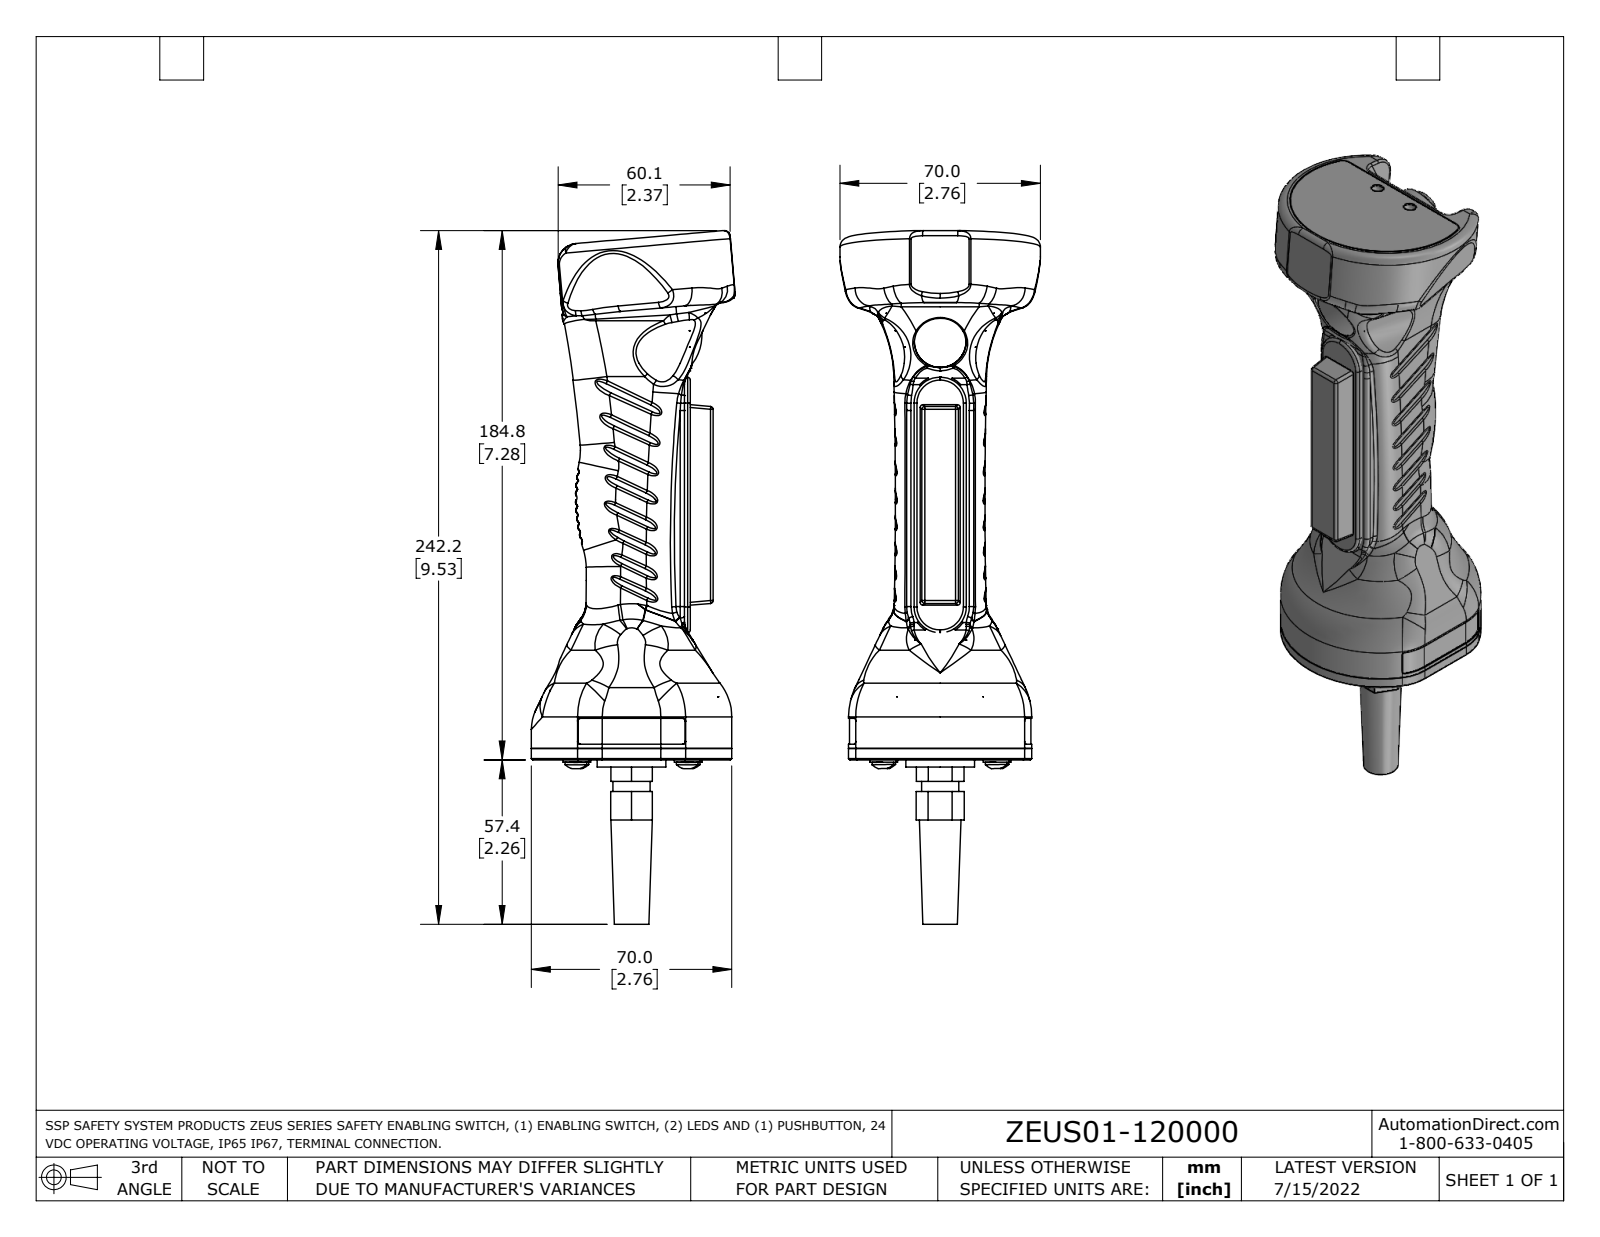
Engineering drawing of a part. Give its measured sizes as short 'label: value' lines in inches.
name: ZEUS01-120000
written by: SolidWorks 2021 (AUTOMOTIVE_DESIGN)
unit: in
bodies: 18 solids, 1363 faces (467 planar, 452 cylindrical, 444 other)
size: 9.535 × 2.803 × 2.756
volume: 23.35 in³; area: 121.2 in²
holes: 4× ⌀0.132, 4× ⌀0.169, 4× ⌀0.177, 4× ⌀0.197, 2× ⌀0.098, 2× ⌀0.11, 2× ⌀0.165, 2× ⌀0.173, 2× ⌀0.331, 1× ⌀0.039, 1× ⌀0.159, 1× ⌀0.201
bosses: 4× ⌀0.354, 4× ⌀0.295, 4× ⌀0.157, 4× ⌀0.039, 2× ⌀0.461, 2× ⌀0.236, 1× ⌀0.945, 1× ⌀0.827
rounds: 96× R0.005, 51× R0.039, 48× R0.028, 22× R0.008, 21× R0.079, 10× R0.118, 8× R0.006, 7× R0.031
face distances: 0.157, 0.079, 0.014, 0.02, 0.065, 0.059, 0.098, 0.177, 0.039, 0.571
hole spacings: 1.531, 0.404, 0.63, 0.866, 0.952, 1.181, 1.558, 2.184
